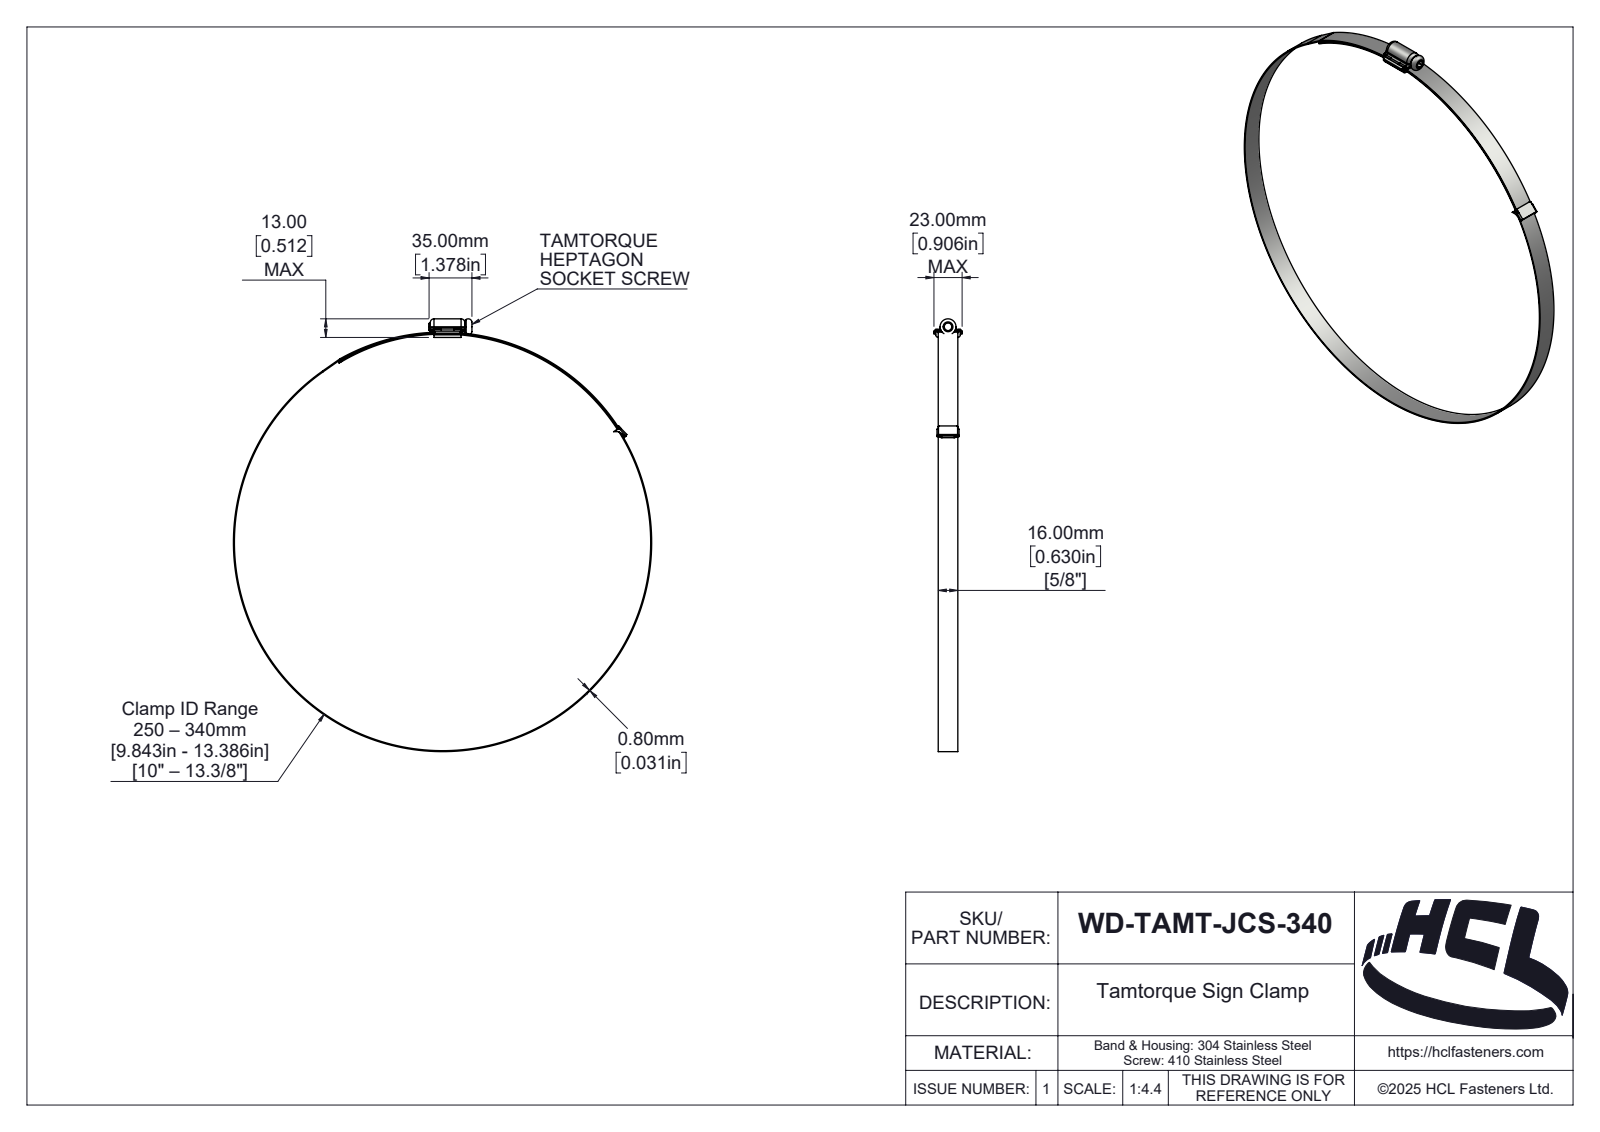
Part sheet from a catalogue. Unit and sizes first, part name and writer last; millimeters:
Units: millimetres
Overall size (bounding box): 353.3 × 341.6 × 23
Round holes (diameter × count): ⌀6 ×1, ⌀340 ×1
Round bosses / shafts (diameter × count): ⌀341.6 ×1, ⌀9 ×1, ⌀5.8 ×1
Partial cylindrical surfaces — rounded edges, fillets, slot ends (radius × count): R0.1 ×28, R1 ×10, R0.5 ×7, R3 ×6, R1.5 ×4, R1.2 ×2, R2.1 ×2, R0.46 ×1
Main face-to-face distances: 16, 2, 4.9, 2.9, 0.8, 18, 1, 3.5, 3, 0.5
Volume: 22 582 mm³ · Surface area: 50 467 mm²
Bodies: 5 solids, 321 faces (101 planar, 139 cylindrical, 81 other)
Part name (STEP PRODUCT): WD-TAMT-JCS-340
STEP written by: SolidWorks 2025 (AUTOMOTIVE_DESIGN)
